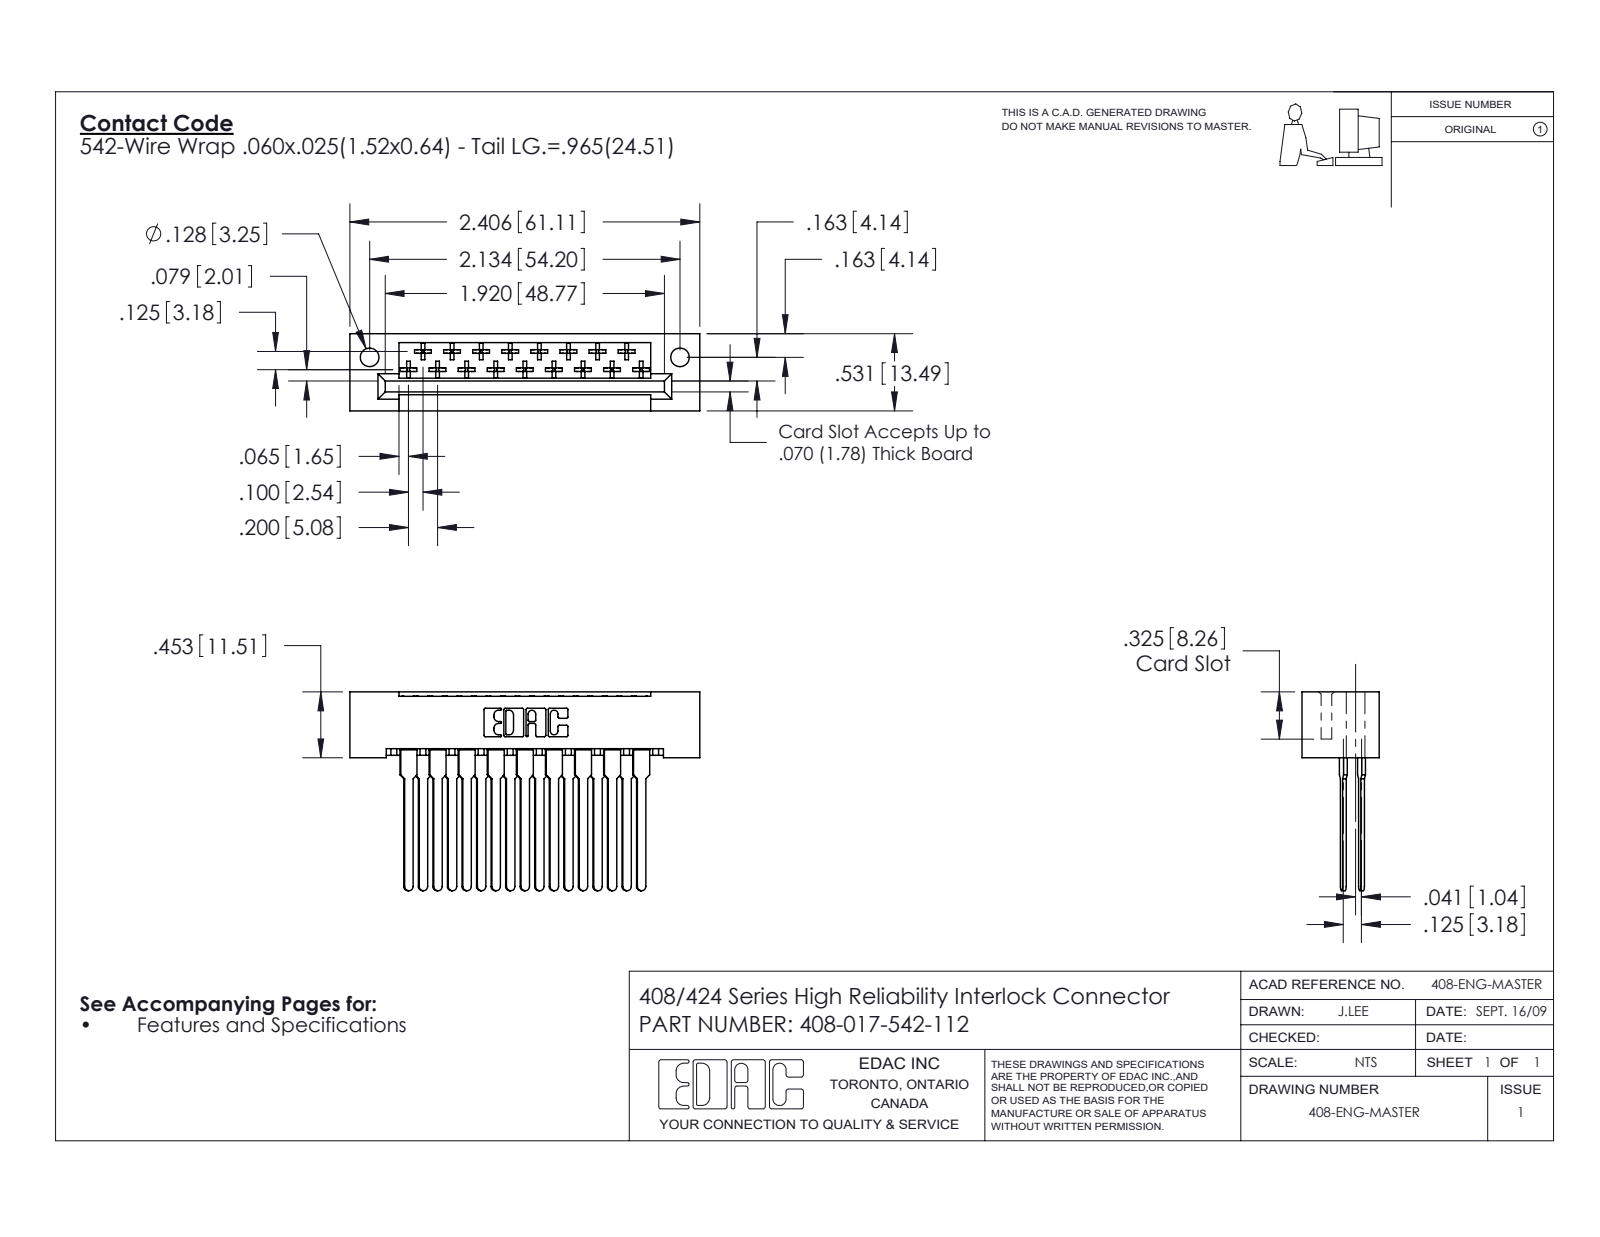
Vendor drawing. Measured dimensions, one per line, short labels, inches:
name: 408-017-542-112; 408 Part_017 - 1; 408-290-001_408-290-142
written by: SolidWorks 2016 (CONFIG_CONTROL_DESIGN)
unit: in
bodies: 18 solids, 1028 faces (759 planar, 201 cylindrical, 68 other)
size: 2.406 × 1.367 × 0.531
volume: 0.461 in³; area: 14.69 in²
holes: 2× ⌀0.128
rounds: 102× R0.01, 22× R0.01, 19× R0.02, 17× R0.03, 6× R0.007, 6× R0.031, 3× R0.026
face distances: 0.025, 0.4, 0.531, 0.104, 0.025, 0.1, 0.095, 0.125, 0.052, 0.235
hole spacings: 2.134
